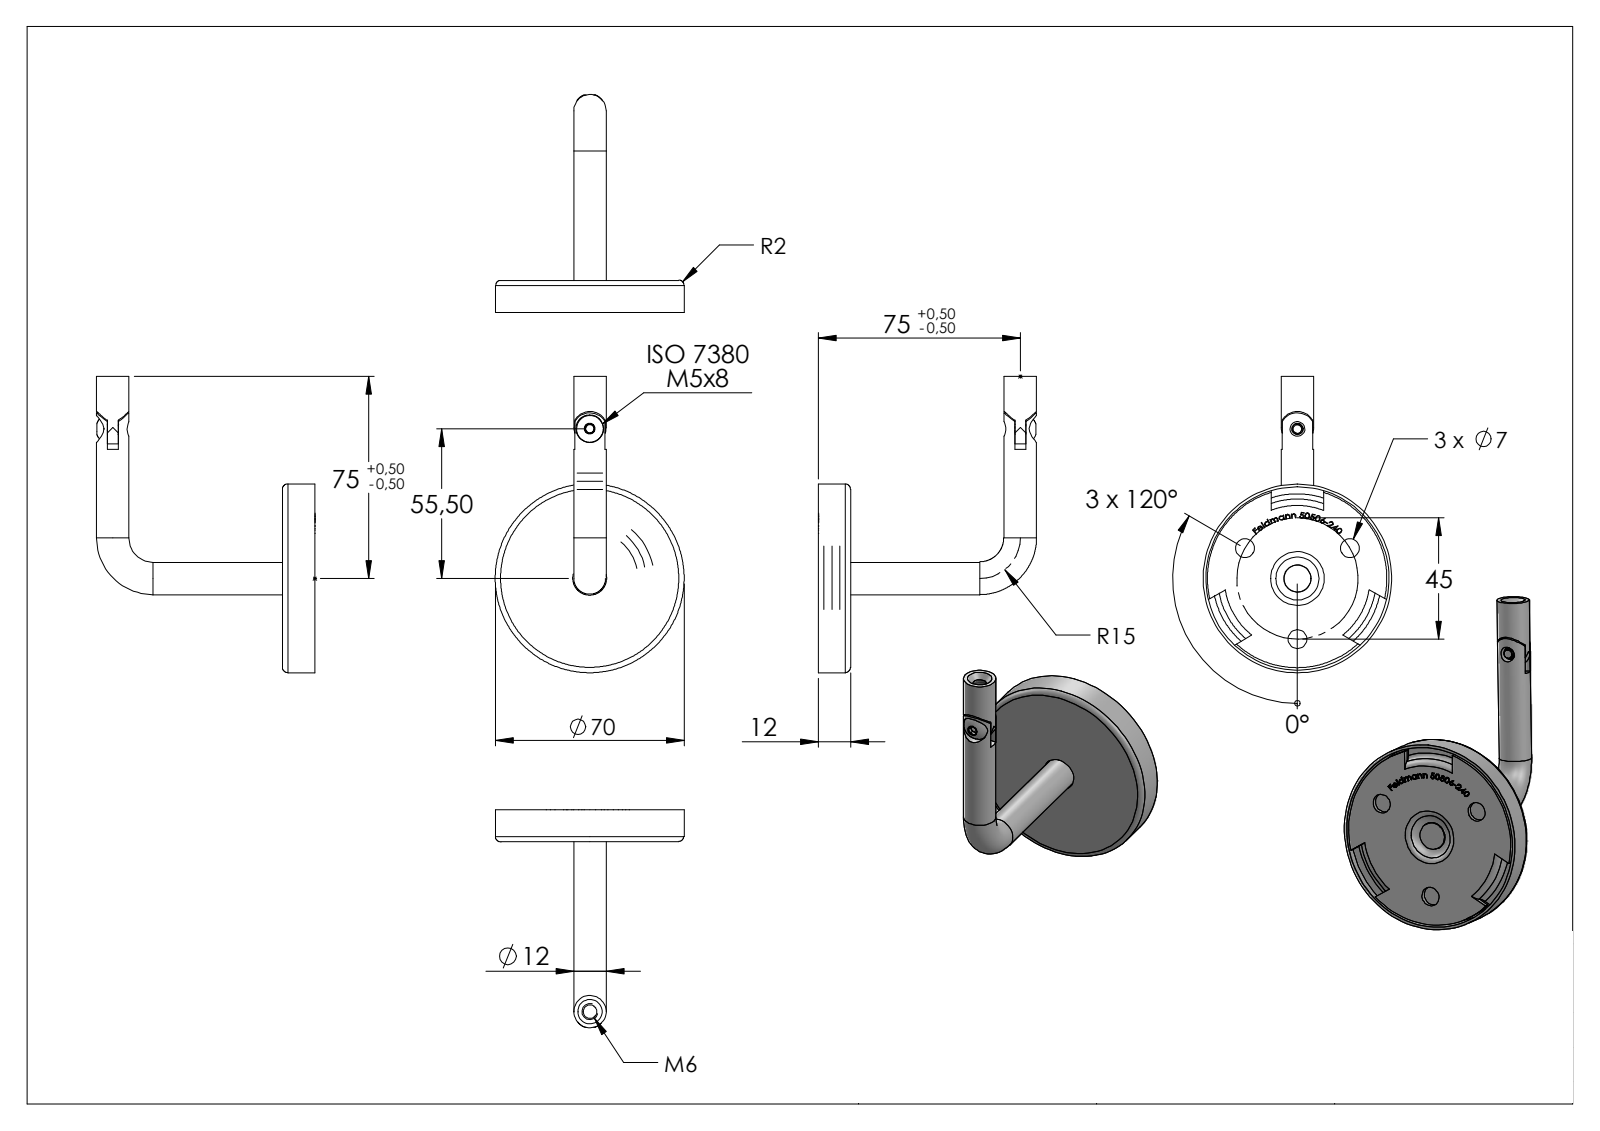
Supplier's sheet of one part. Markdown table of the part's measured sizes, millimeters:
| quantity | value |
| --- | --- |
| part name | 5050X-240 Teil3_50500-240-AR; 5050X-240 Teil5_5050X-240 Teil5; 50506-240; 5050X-240 Teil6_ISO 7380 M5x8 (+2 more) |
| STEP written by | SolidWorks 2018 (CONFIG_CONTROL_DESIGN) |
| units | millimeters |
| bodies | 5 solids, 338 faces (160 planar, 38 cylindrical, 140 other) |
| overall size | 110 × 81 × 70 |
| volume | 28 143 mm³ |
| surface area | 26 699 mm² |
| round holes (diameter × count) | 7 × 3, 4.2 × 1, 5 × 1, 5.5 × 1, 10 × 1, 10.1 × 1, 12.4 × 1 |
| round bosses / shafts (diameter × count) | 12 × 2, 70 × 1, 68 × 1, 10 × 1, 9 × 1, 4.02 × 1 |
| partial cylindrical surfaces (radius × count) | 6.5 × 2, 6 × 1, 33.25 × 1 |
| main face-to-face distances | 1, 11, 12, 2, 9, 10, 3.2, 66.05, 4.05, 1.2 |
| hole center spacings | 22.5, 38.97, 48.35, 38.98, 55.5, 78 |
